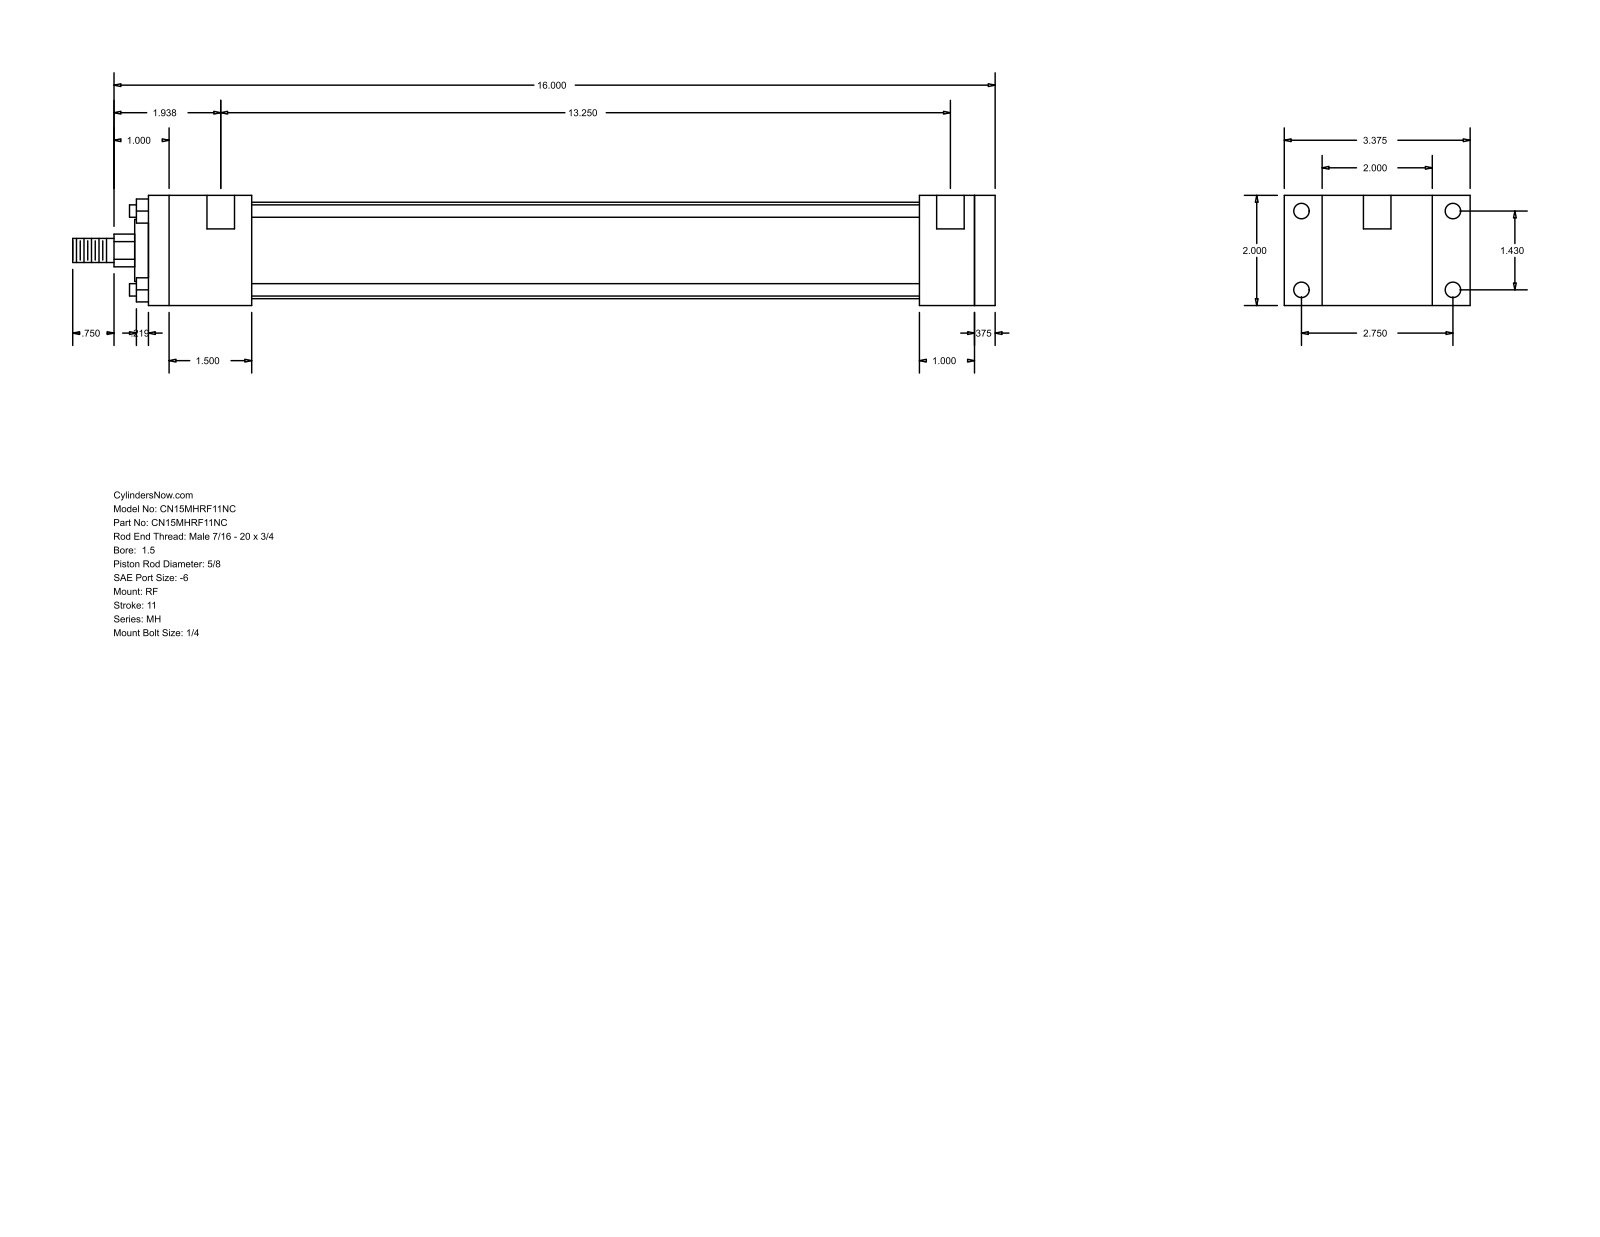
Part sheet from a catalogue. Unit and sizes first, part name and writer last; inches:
Units: inches
Overall size (bounding box): 16.75 × 3.375 × 2
Round holes (diameter × count): ⌀0.219 ×4, ⌀0.281 ×4, ⌀0.5 ×2
Round bosses / shafts (diameter × count): ⌀0.225 ×4, ⌀1.75 ×1, ⌀1.125 ×1, ⌀0.625 ×1, ⌀0.437 ×1
Partial cylindrical surfaces — rounded edges, fillets, slot ends (radius × count): R0.297 ×1
Main face-to-face distances: 2, 0.375, 15, 15.375, 1, 0.687, 2.687, 14, 1.375, 1.875
Hole centre spacings: 1.43, 2.75, 3.099, 13.375, 0.125, 13.25
Bodies: 0 solids, 92 faces (64 planar, 28 cylindrical, 0 other)
Part name (STEP PRODUCT): MH_RF__0150_0.625
STEP written by: GSSL Pune (CONFIG_CONTROL_DESIGN)
